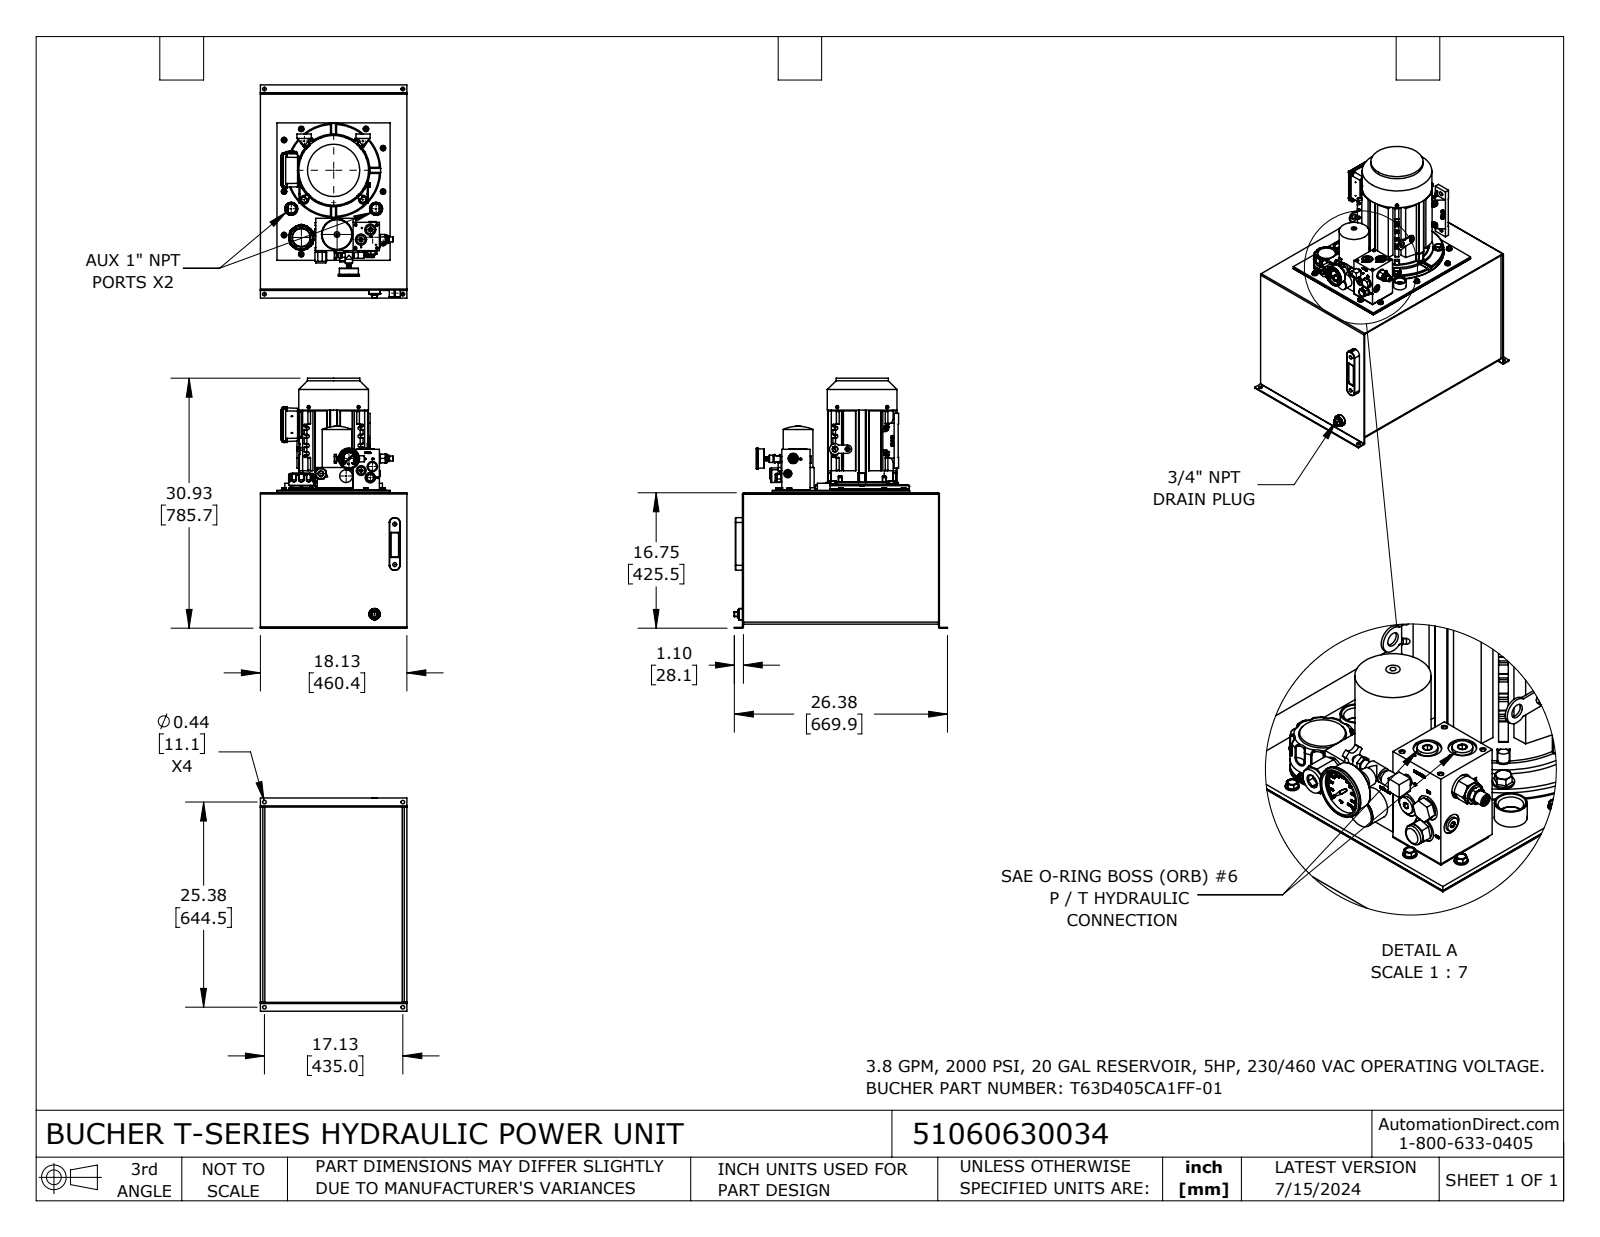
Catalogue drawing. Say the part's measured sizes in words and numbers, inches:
The part is named "51060630034". Its 3-D file was written by "SolidWorks 2023 (CONFIG_CONTROL_DESIGN)". It is 129 solids with 7004 faces: 3495 planar, 1924 cylindrical and 1585 other. Overall it measures 30.932 by 26.4 by 18.125 inches. Its volume is 1 239 cubic inches and its surface area 6 620 square inches. Round holes: 19 of diameter 0.437, 15 of diameter 0.5, 13 of diameter 0.257, 11 of diameter 0.236, 9 of diameter 0.197, 8 of diameter 0.201, 6 of diameter 0.19, 6 of diameter 0.315, 6 of diameter 0.472, 6 of diameter 0.531, 6 of diameter 0.563, 5 of diameter 0.75. Round bosses or shafts: 13 of diameter 0.313, 10 of diameter 0.676, 9 of diameter 0.365, 8 of diameter 0.197, 8 of diameter 0.157, 6 of diameter 0.551, 6 of diameter 0.472, 6 of diameter 0.373. Partial cylindrical surfaces (rounded edges, fillets, slot ends): 116 of radius 0.079, 112 of radius 0.02, 60 of radius 0.039, 49 of radius 0.05, 36 of radius 0.25, 20 of radius 0.063, 20 of radius 0.118, 20 of radius 0.167. The main face-to-face distances are 0.104, 16.135, 24.27, 0.105, 17.5, 17.395, 17.291, 17.396, 16.239, 24.375. The hole center spacings are 3.15, 3.469, 7.339, 5.262, 0.78, 1.467, 2.005, 2.874.
